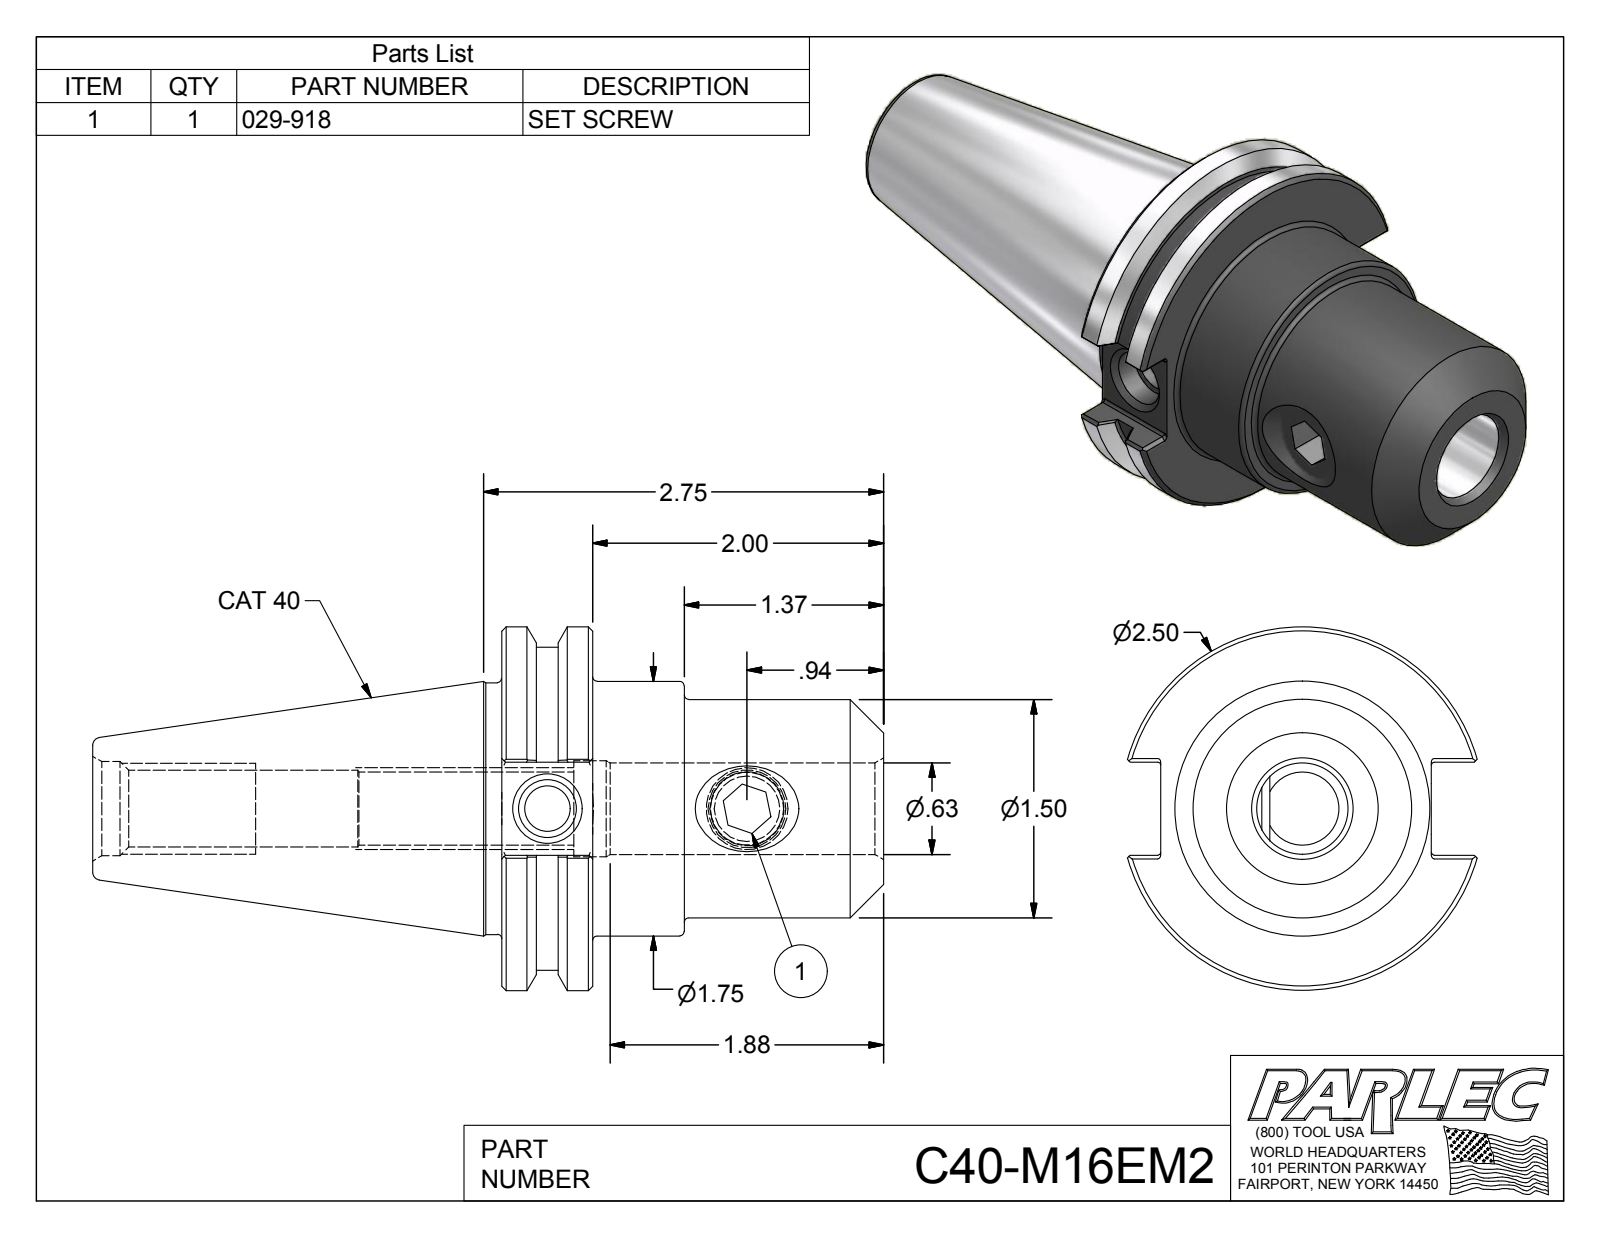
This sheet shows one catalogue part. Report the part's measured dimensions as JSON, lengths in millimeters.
{"part_name": "C40-M16EM2; C40-M16EM2-1; 029-918", "step_written_by": "Autodesk Inventor 2012 (AUTOMOTIVE_DESIGN)", "units": "millimeters", "bodies": {"solids": 2, "faces": 106, "planar": 42, "cylindrical": 30, "other": 34}, "overall_size": [138.1, 63.5, 61.1], "volume_mm3": 152600, "surface_area_mm2": 29710, "round_holes": [[12.8, 2], [8, 1], [10.1, 1], [13.4, 1], [16, 1], [16.5, 1], [16.8, 1]], "round_bosses_or_shafts": [[63.5, 1], [56.4, 1], [44.5, 1], [43.9, 1], [38.1, 1], [14.3, 1]], "partial_cylinders_radius": [[0.5, 12]], "face_to_face_distances": [15.9, 66.7, 50.8, 31.9, 16, 34.8, 16.3, 47.2, 71.4, 87.3], "hole_center_spacings": [34.8]}
